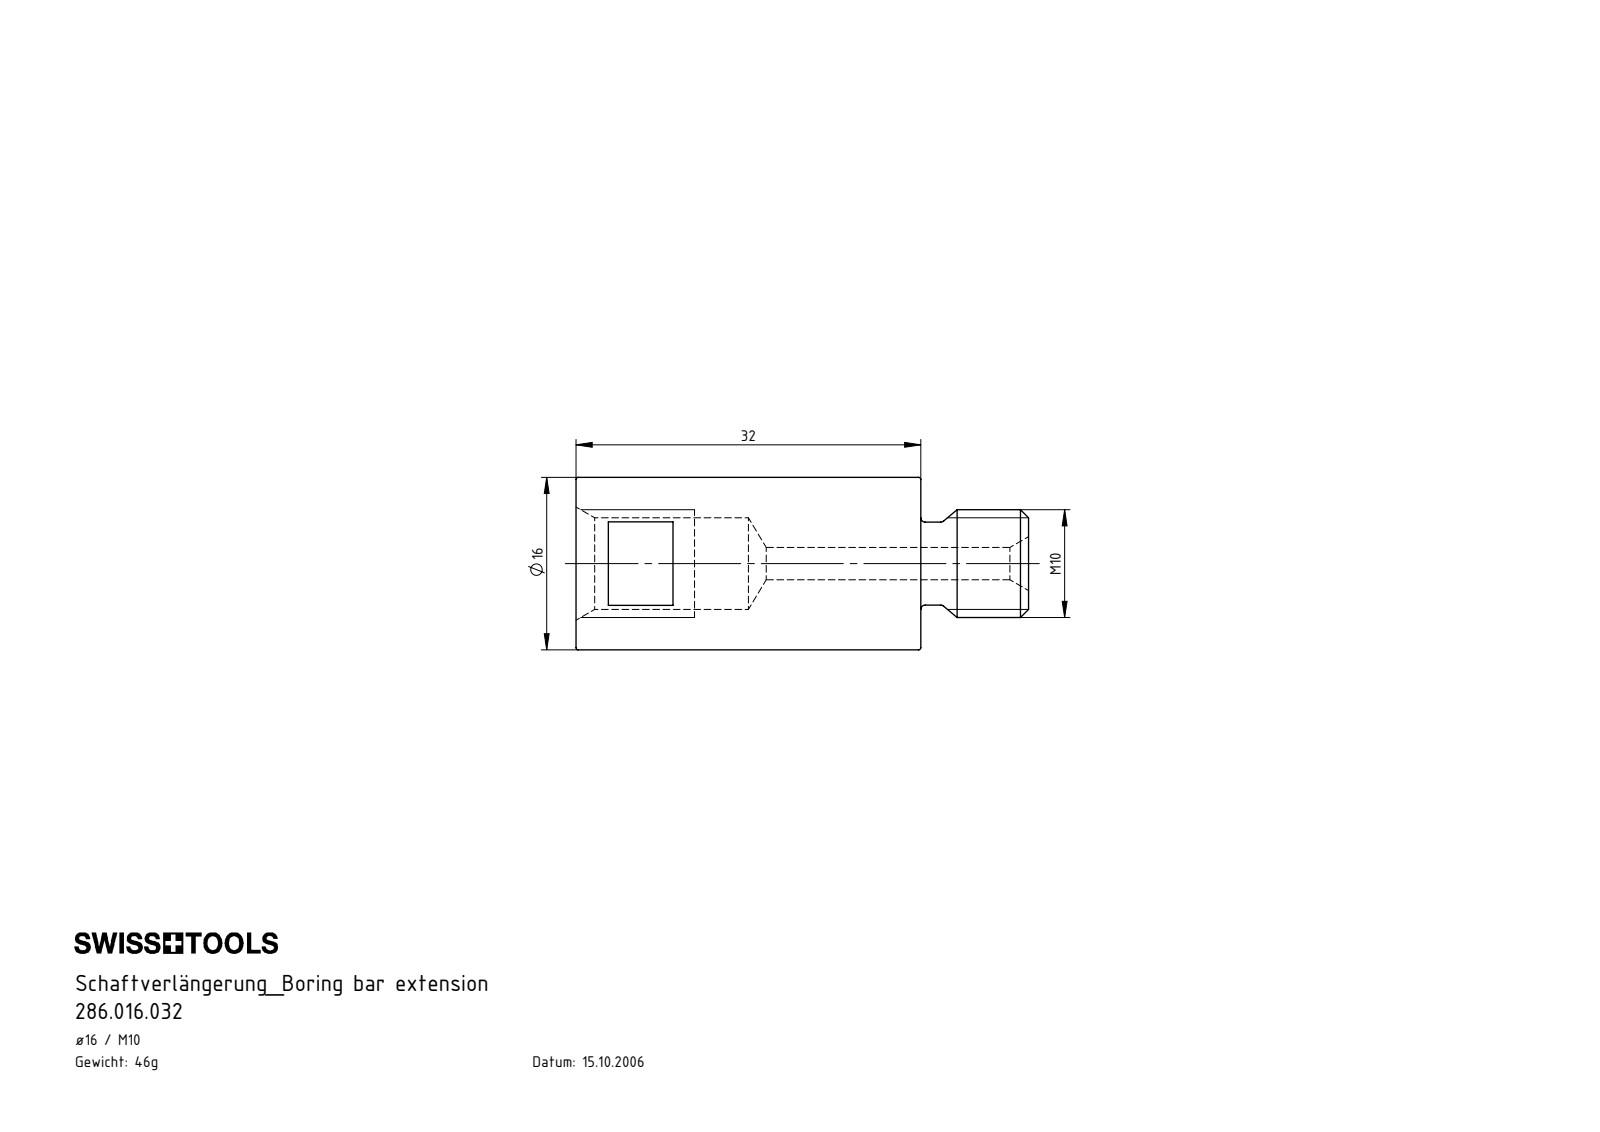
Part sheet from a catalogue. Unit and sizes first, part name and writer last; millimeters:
Units: millimetres
Overall size (bounding box): 42 × 16 × 16
Round holes (diameter × count): ⌀3 ×1, ⌀8.5 ×1
Round bosses / shafts (diameter × count): ⌀16 ×1, ⌀10 ×1, ⌀7.7 ×1
Main face-to-face distances: 32, 14, 10, 42, 39, 29, 3, 33, 23, 6
Volume: 5 900 mm³ · Surface area: 2 969 mm²
Bodies: 1 solid, 37 faces (9 planar, 10 cylindrical, 18 other)
Part name (STEP PRODUCT): HS0-U16.K01.032_A
STEP written by: SolidWorks 2017 (CONFIG_CONTROL_DESIGN)
